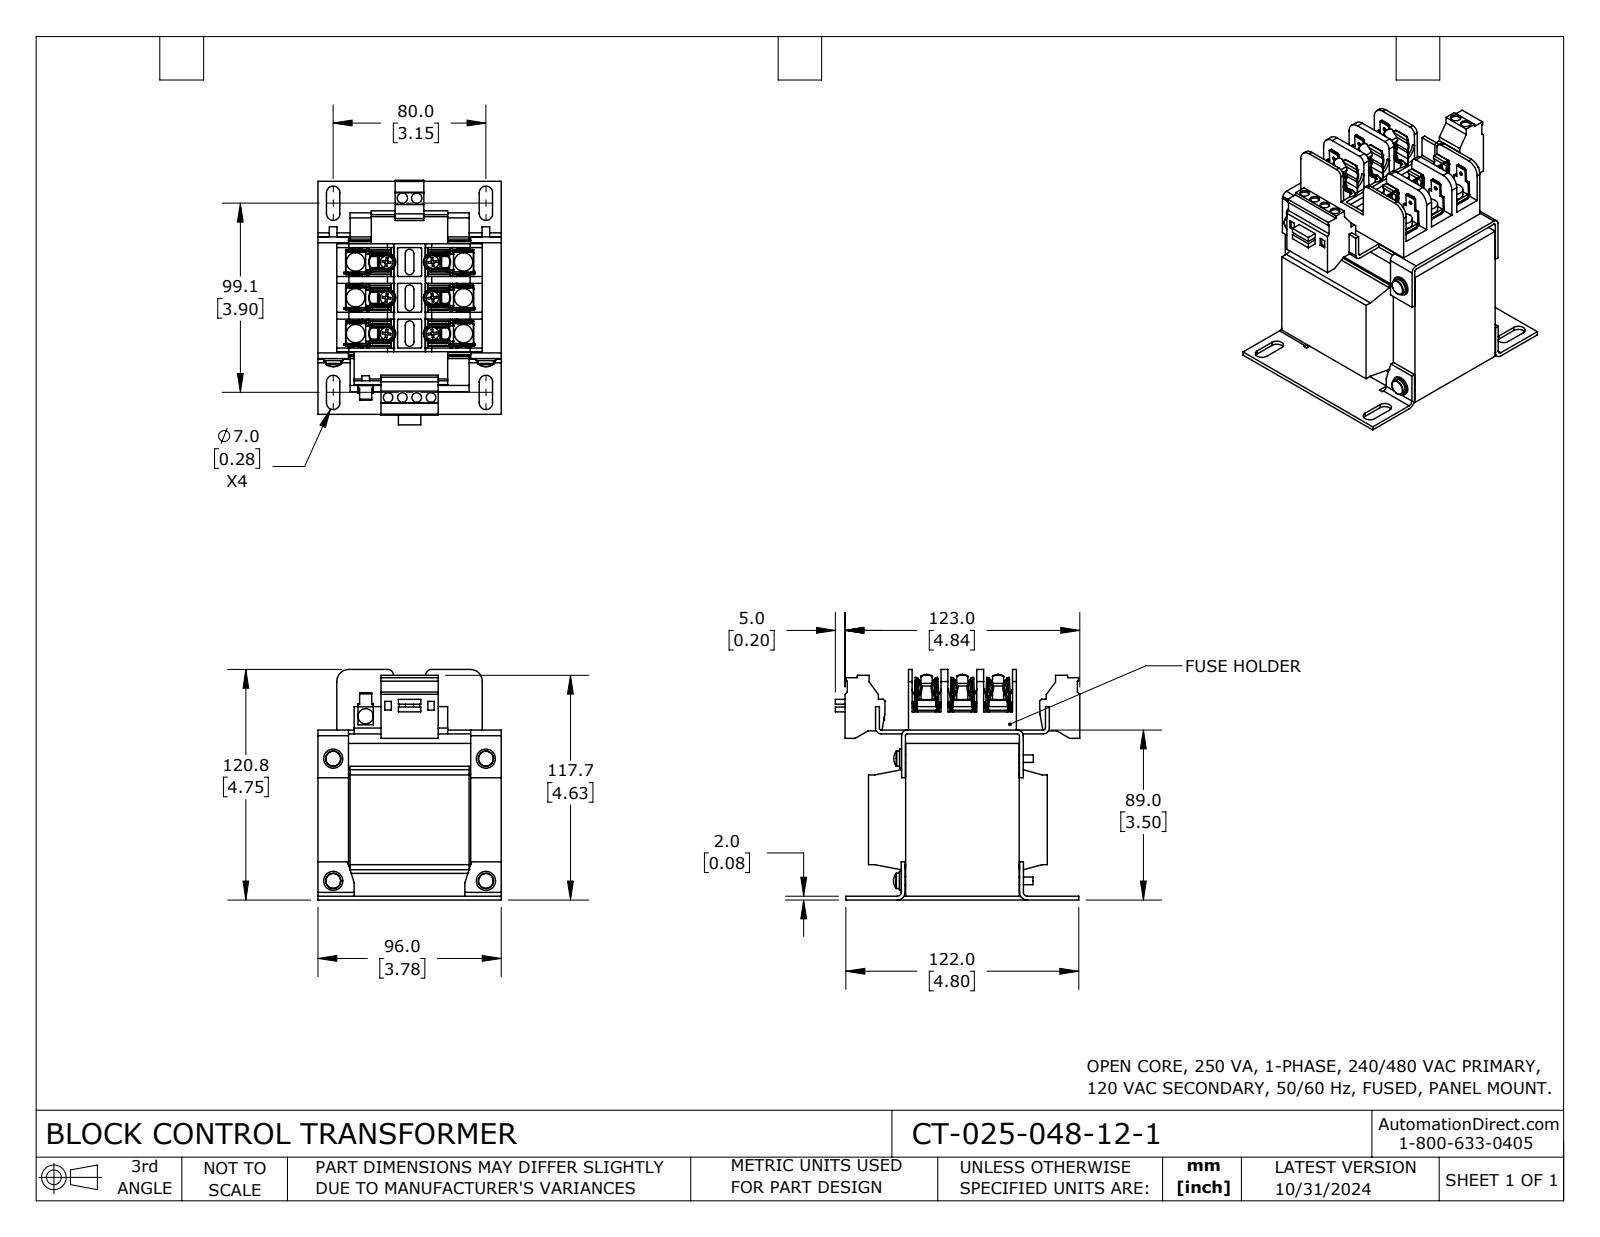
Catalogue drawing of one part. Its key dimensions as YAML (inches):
part_name: "CT-025-048-12-1"
step_written_by: "SolidWorks 2023 (CONFIG_CONTROL_DESIGN)"
units: inches
bodies: {solids: 2, faces: 1598, planar: 1029, cylindrical: 527, other: 42}
overall_size: [5.039, 4.754, 3.78]
volume: 41.77
surface_area: 223.2
round_holes:
  - {diameter: 0.074, count: 12}
  - {diameter: 0.205, count: 5}
  - {diameter: 0.197, count: 4}
  - {diameter: 0.213, count: 2}
  - {diameter: 0.205, count: 1}
round_bosses_or_shafts:
  - {diameter: 0.38, count: 6}
  - {diameter: 0.19, count: 6}
  - {diameter: 0.315, count: 5}
  - {diameter: 0.157, count: 5}
  - {diameter: 0.394, count: 4}
  - {diameter: 0.177, count: 4}
partial_cylinders:
  - {radius: 0.01, count: 24}
  - {radius: 0.05, count: 20}
  - {radius: 0.03, count: 18}
  - {radius: 0.072, count: 14}
  - {radius: 0.038, count: 12}
  - {radius: 0.04, count: 12}
  - {radius: 0.164, count: 12}
  - {radius: 0.097, count: 9}
face_to_face_distances: [0.079, 3.425, 3.15, 0.63, 0.661, 3.118, 3.504, 2.52, 3.346, 0.197]
hole_center_spacings: [2.232, 2.354, 0.026, 0.026, 0.052, 0.295, 0.738, 1.633]
